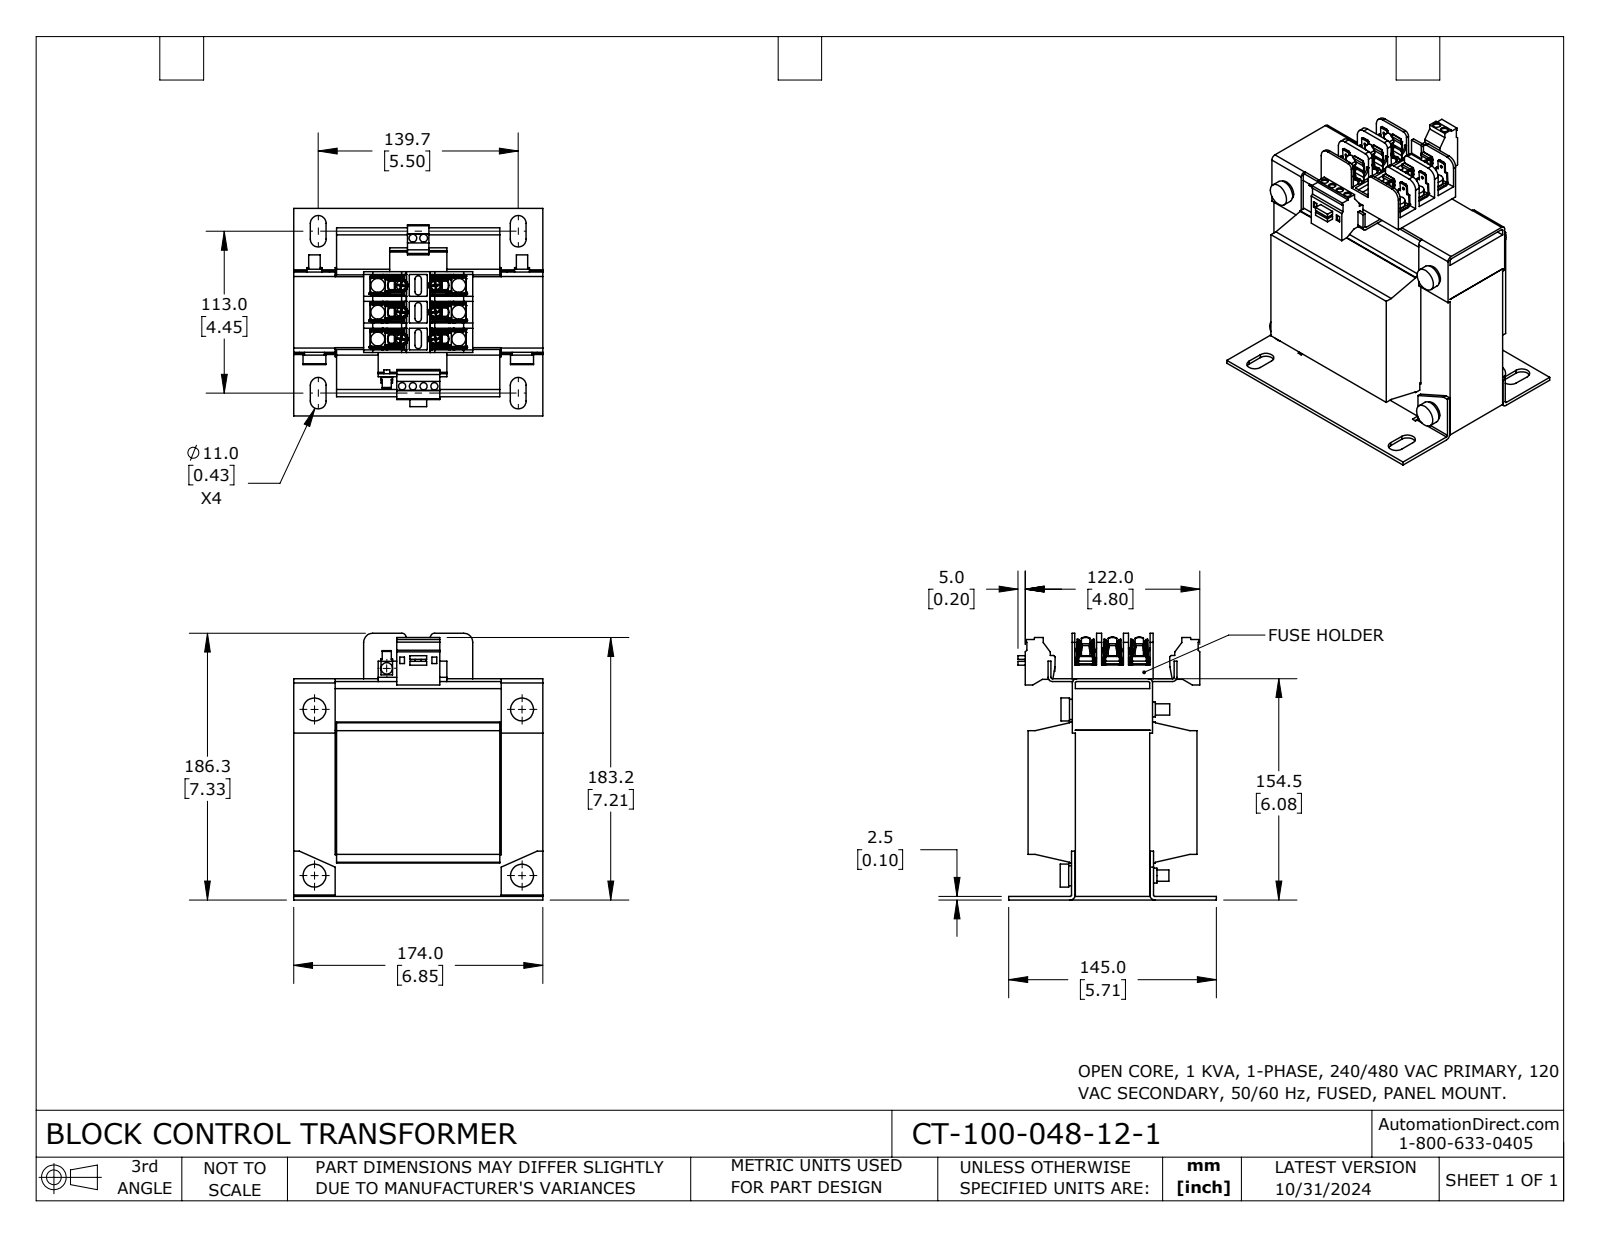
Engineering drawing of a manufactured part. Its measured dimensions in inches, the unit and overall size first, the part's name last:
Units: inches
Overall size (bounding box): 7.333 × 6.85 × 5.709
Round holes (diameter × count): ⌀0.074 ×12, ⌀0.205 ×5, ⌀0.197 ×4, ⌀0.213 ×2, ⌀0.205 ×1
Round bosses / shafts (diameter × count): ⌀0.38 ×6, ⌀0.19 ×6, ⌀0.315 ×5, ⌀0.63 ×4, ⌀0.551 ×4, ⌀0.413 ×4, ⌀0.394 ×2, ⌀0.157 ×1
Partial cylindrical surfaces — rounded edges, fillets, slot ends (radius × count): R0.01 ×24, R0.05 ×20, R0.03 ×18, R0.072 ×14, R0.038 ×12, R0.04 ×12, R0.164 ×12, R0.097 ×9
Main face-to-face distances: 4.567, 1.142, 0.098, 1.299, 3.346, 5.709, 1.181, 5.669, 4.665, 0.079
Hole centre spacings: 2.232, 2.354, 0.026, 0.295, 0.738, 1.617, 1.809, 2.253
Volume: 133.1 in³ · Surface area: 407.4 in²
Bodies: 2 solids, 1600 faces (1039 planar, 531 cylindrical, 30 other)
Part name (STEP PRODUCT): CT-100-048-12-1
STEP written by: SolidWorks 2023 (CONFIG_CONTROL_DESIGN)
